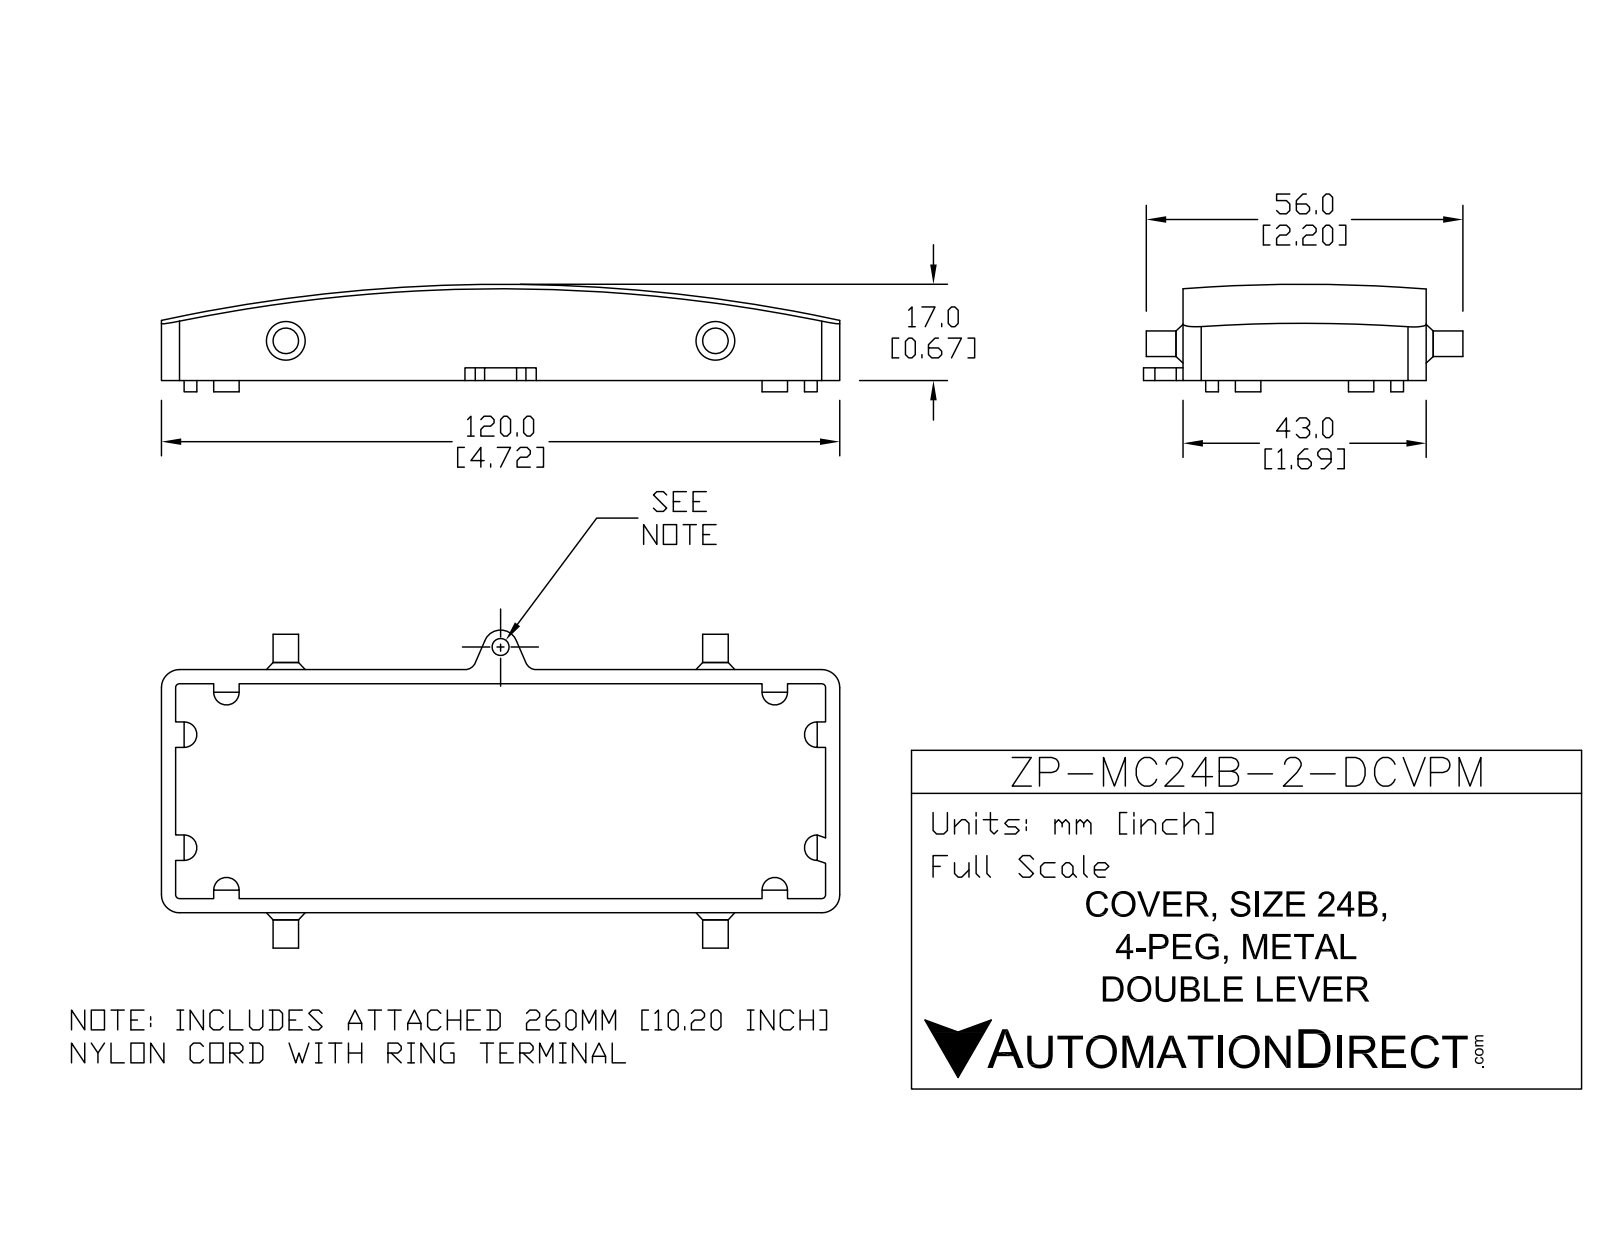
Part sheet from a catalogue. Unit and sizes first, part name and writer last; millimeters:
Units: millimetres
Overall size (bounding box): 120 × 56.25 × 18.5
Round holes (diameter × count): ⌀3 ×1
Round bosses / shafts (diameter × count): ⌀4.52 ×2
Partial cylindrical surfaces — rounded edges, fillets, slot ends (radius × count): R2.25 ×8, R0.7 ×4, R3.2 ×4, R2 ×2, R3 ×1
Main face-to-face distances: 2.5, 40.5, 43, 38, 117.5, 120, 115, 1.25, 3.75, 41.75
Volume: 22 755 mm³ · Surface area: 19 098 mm²
Bodies: 9 solids, 98 faces (68 planar, 24 cylindrical, 6 other)
Part name (STEP PRODUCT): ZP-MC24B-2-DCVPM
STEP written by: SolidWorks 2011 (AUTOMOTIVE_DESIGN)
